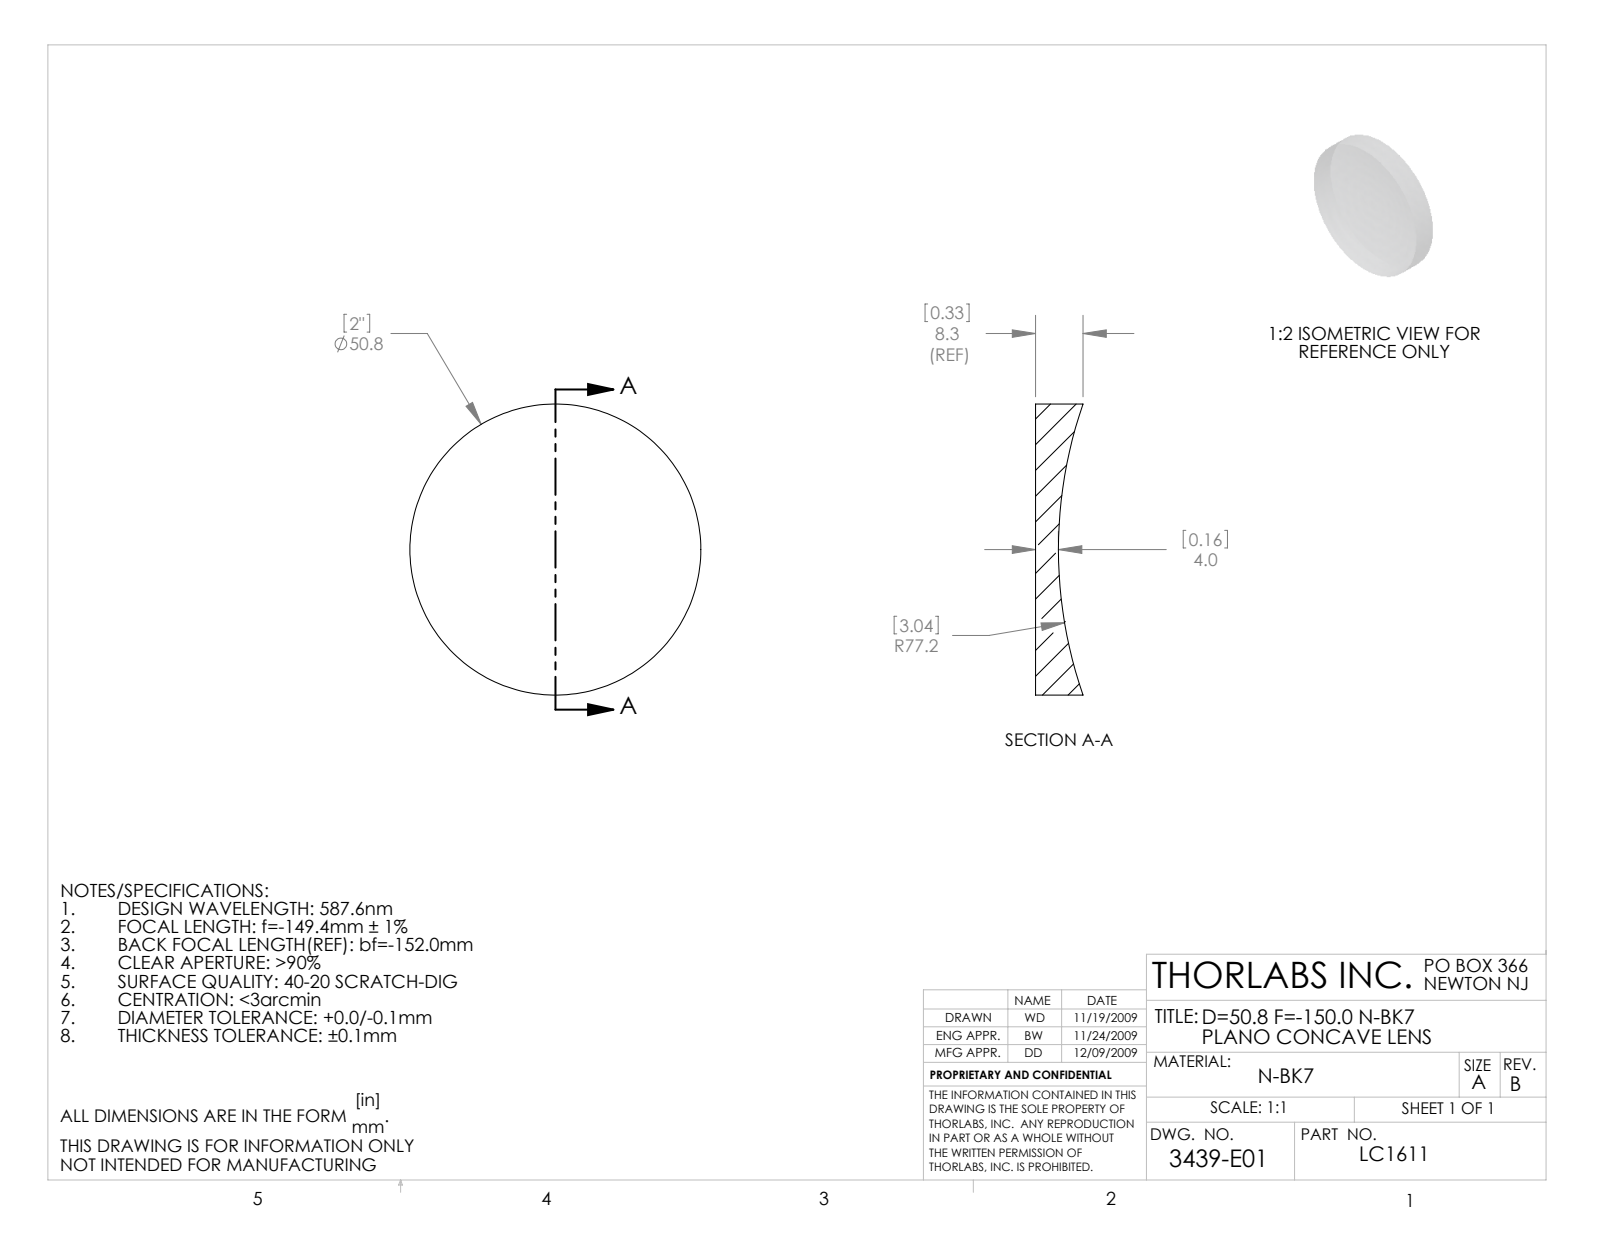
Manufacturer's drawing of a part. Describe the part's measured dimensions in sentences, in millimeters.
The part is named "3439-E0W". Its 3-D file was written by "SolidWorks 2009 (AUTOMOTIVE_DESIGN)". It is 1 solid with 5 faces: 1 planar, 2 cylindrical and 2 other. Overall it measures 50.8 by 50.8 by 8.3 millimeters. Its volume is 12 422 cubic millimeters and its surface area 5 436 square millimeters. Round bosses or shafts: 1 of diameter 50.8.
